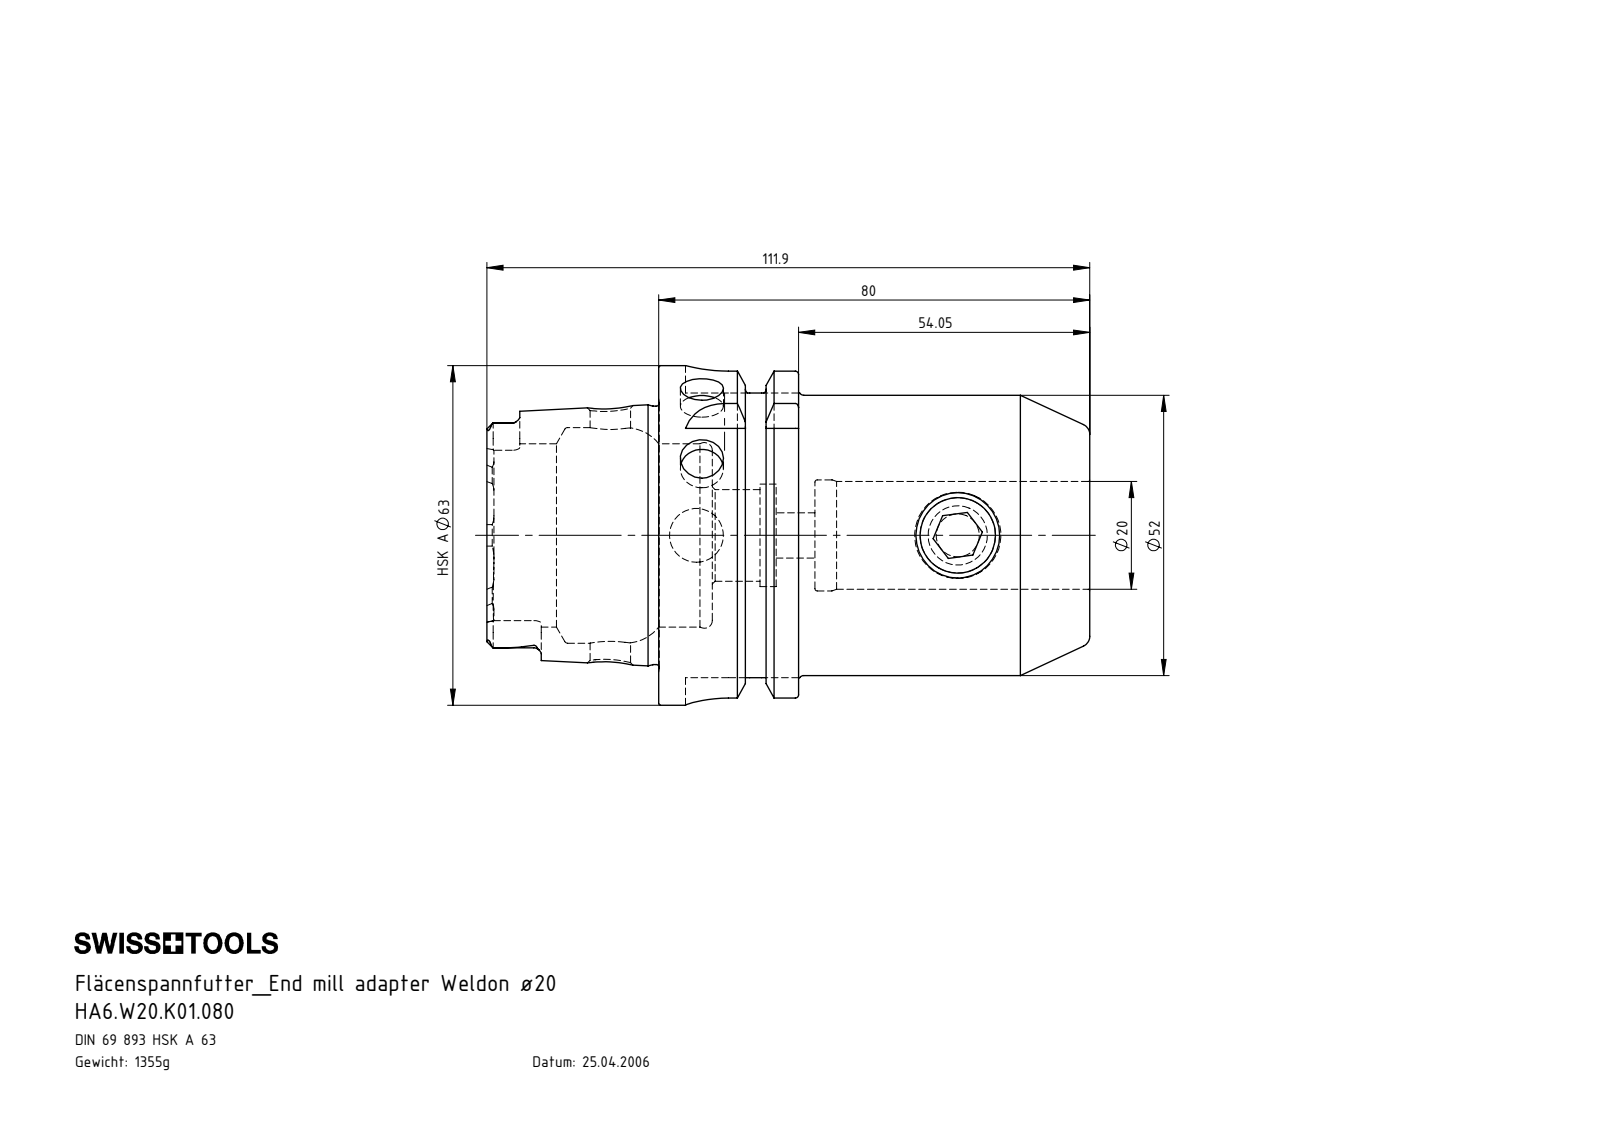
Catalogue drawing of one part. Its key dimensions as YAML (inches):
part_name: "HA6.W20.K01.080; W20-ER1.001.016; HA6-W20.K01.080_C_Fertigbearbeitung"
step_written_by: "SolidWorks 2012 (CONFIG_CONTROL_DESIGN)"
units: inches
bodies: {solids: 2, faces: 209, planar: 59, cylindrical: 57, other: 93}
overall_size: [4.406, 2.48, 2.48]
volume: 10.53
surface_area: 55
round_holes:
  - {diameter: 0.315, count: 2}
  - {diameter: 0.295, count: 1}
  - {diameter: 0.331, count: 1}
  - {diameter: 0.394, count: 1}
  - {diameter: 0.551, count: 1}
  - {diameter: 0.669, count: 1}
  - {diameter: 0.748, count: 1}
  - {diameter: 0.787, count: 1}
  - {diameter: 0.811, count: 1}
  - {diameter: 1.339, count: 1}
  - {diameter: 1.575, count: 1}
round_bosses_or_shafts:
  - {diameter: 2.48, count: 1}
  - {diameter: 2.163, count: 1}
  - {diameter: 2.047, count: 1}
  - {diameter: 1.887, count: 1}
  - {diameter: 0.63, count: 1}
partial_cylinders:
  - {radius: 0.055, count: 6}
  - {radius: 0.113, count: 4}
  - {radius: 0.315, count: 4}
face_to_face_distances: [3.15, 1.022, 2.128, 0.63, 0.392, 2.758, 1.256, 1.648, 2.278, 4.406]
hole_center_spacings: [1.909]
